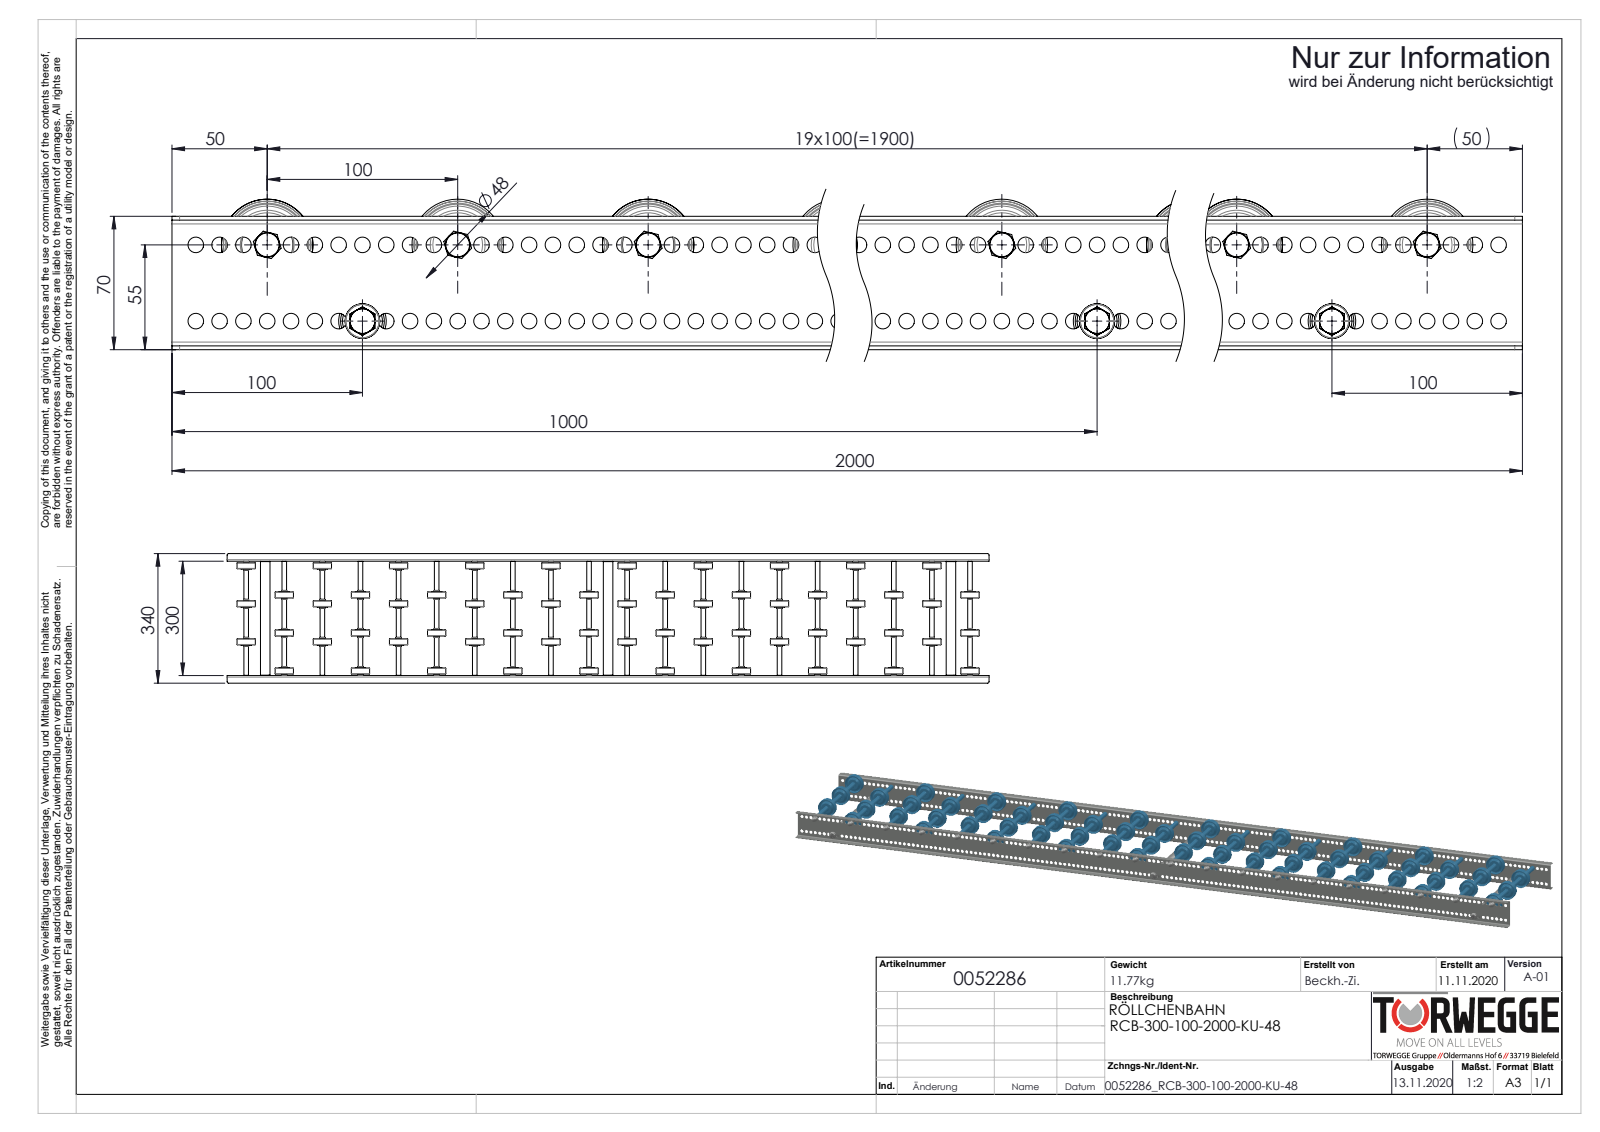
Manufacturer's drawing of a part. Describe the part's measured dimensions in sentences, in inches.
The part is named "0052286; 0011532_2300-48-8; S106837_Gewindestange-M8-KFG_L320; 0046278_KB-ROHR-12X1,75mm_KFG_L76 (+5 more)". Its 3-D file was written by "SolidWorks 2020 (AUTOMOTIVE_DESIGN)". It is 197 solids with 7446 faces: 1302 planar, 2868 cylindrical and 3276 other. Overall it measures 78.74 by 13.386 by 3.11 inches. Its volume is 159.9 cubic inches and its surface area 3 174 square inches. Round holes: 318 of diameter 0.323, 20 of diameter 0.262, 20 of diameter 0.38, 20 of diameter 0.539, 3 of diameter 0.268, 3 of diameter 0.827. Round bosses or shafts: 23 of diameter 0.315, 20 of diameter 1.89, 20 of diameter 1.063, 20 of diameter 0.5, 20 of diameter 0.492, 20 of diameter 0.472, 3 of diameter 0.984. Partial cylindrical surfaces (rounded edges, fillets, slot ends): 8 of radius 0.157, 4 of radius 0.079. The main face-to-face distances are 0.079, 11.89, 2.677, 11.969, 11.811, 2.756, 2.598, 3.929, 0.642, 2.996. The hole center spacings are 0.492, 0.984, 1.476, 1.969, 2.461, 2.953, 3.445, 3.937.
